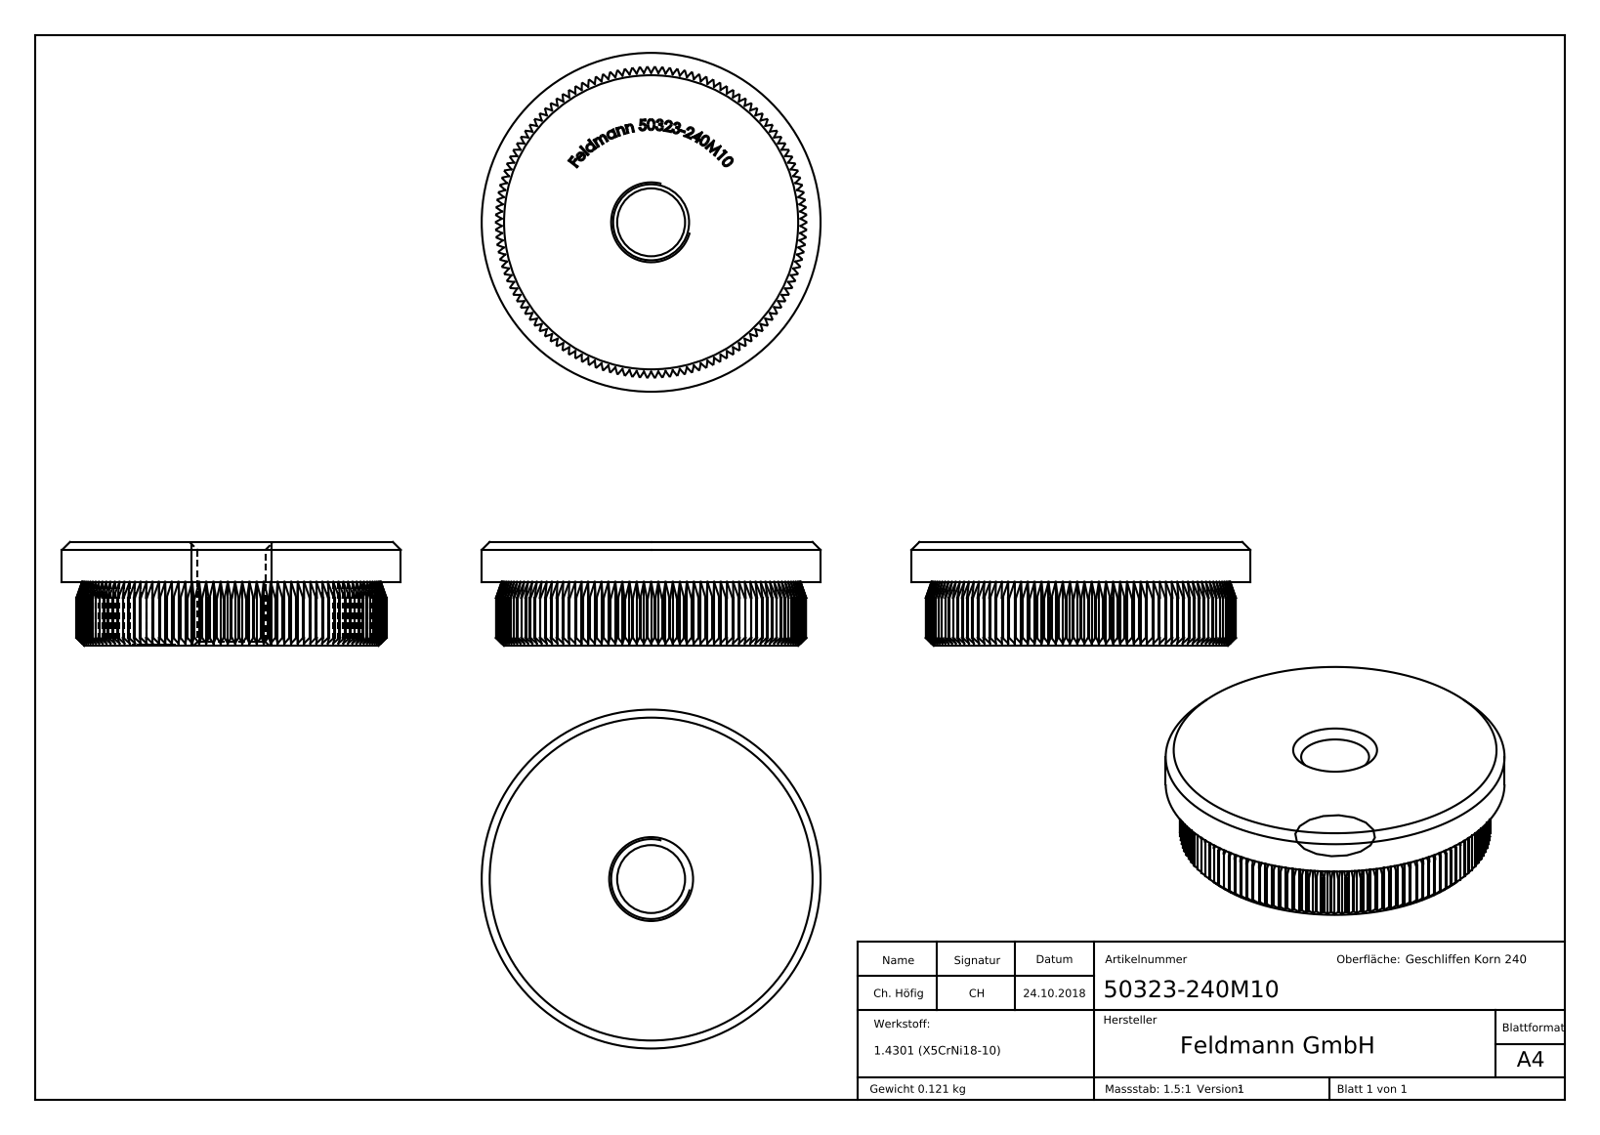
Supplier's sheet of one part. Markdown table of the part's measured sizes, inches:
| quantity | value |
| --- | --- |
| part name | 50323-240M10 |
| STEP written by | SolidWorks 2015 (CONFIG_CONTROL_DESIGN) |
| units | inches |
| bodies | 1 solid, 821 faces (410 planar, 134 cylindrical, 277 other) |
| overall size | 1.669 × 1.669 × 0.512 |
| volume | 0.936 in³ |
| surface area | 8.173 in² |
| round holes (diameter × count) | 0.335 × 1 |
| round bosses / shafts (diameter × count) | 1.669 × 1 |
| partial cylindrical surfaces (radius × count) | 0.764 × 1 |
| main face-to-face distances | 0.512, 0.736, 0.315, 0.197, 0.737, 0.735, 0.311, 0.508, 0.021, 0.026 |
